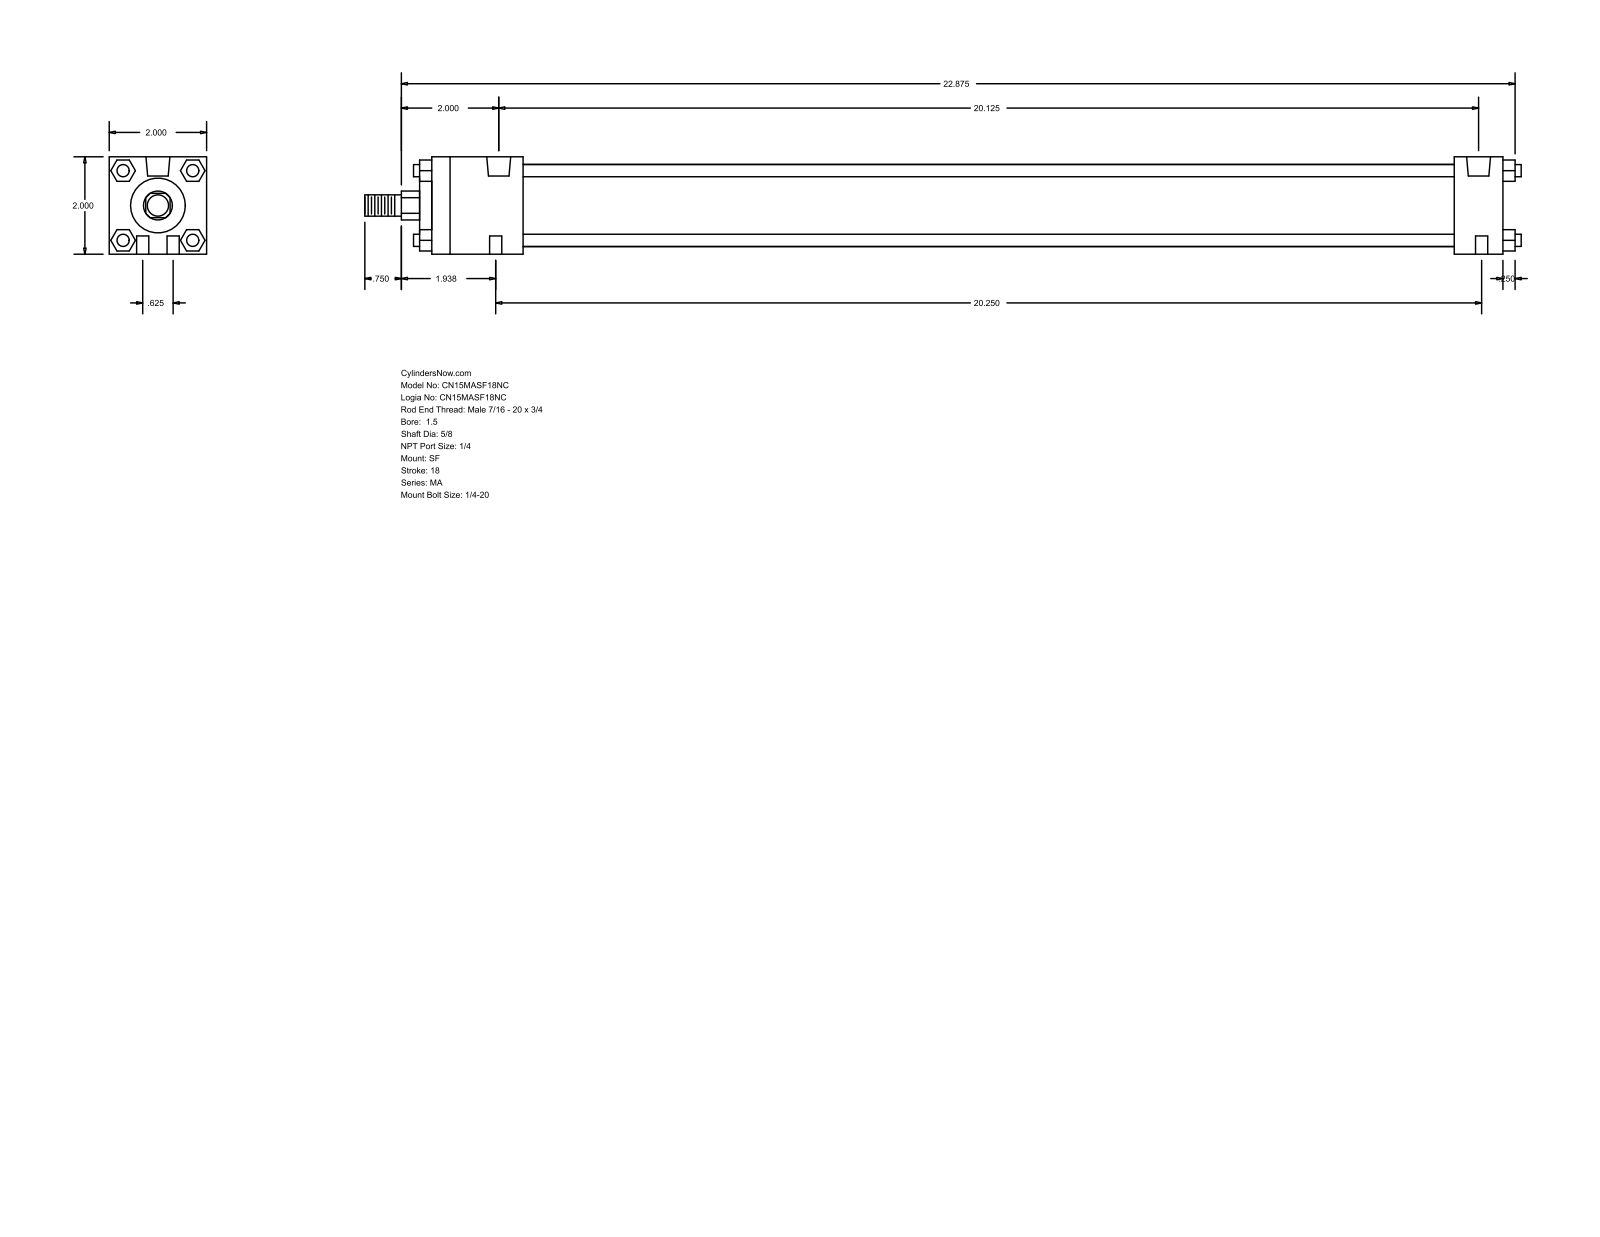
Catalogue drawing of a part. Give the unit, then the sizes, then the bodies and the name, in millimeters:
Units: millimetres
Overall size (bounding box): 603.25 × 50.8 × 50.8
Round holes (diameter × count): ⌀6.35 ×4, ⌀7.94 ×2, ⌀12.49 ×2
Round bosses / shafts (diameter × count): ⌀6.35 ×4, ⌀42.93 ×1, ⌀28.57 ×1, ⌀15.88 ×1, ⌀11.11 ×1
Partial cylindrical surfaces — rounded edges, fillets, slot ends (radius × count): R7.54 ×1
Main face-to-face distances: 50.8, 558.79, 6.35, 25.4, 565.14, 47.62, 533.39, 485.77, 511.17, 53.97
Hole centre spacings: 8.1, 15.88, 511.18, 512.82, 512.83, 514.35, 514.6
Bodies: 0 solids, 124 faces (94 planar, 30 cylindrical, 0 other)
Part name (STEP PRODUCT): MA_SF__0150_0.625
STEP written by: GSSL Pune (CONFIG_CONTROL_DESIGN)
